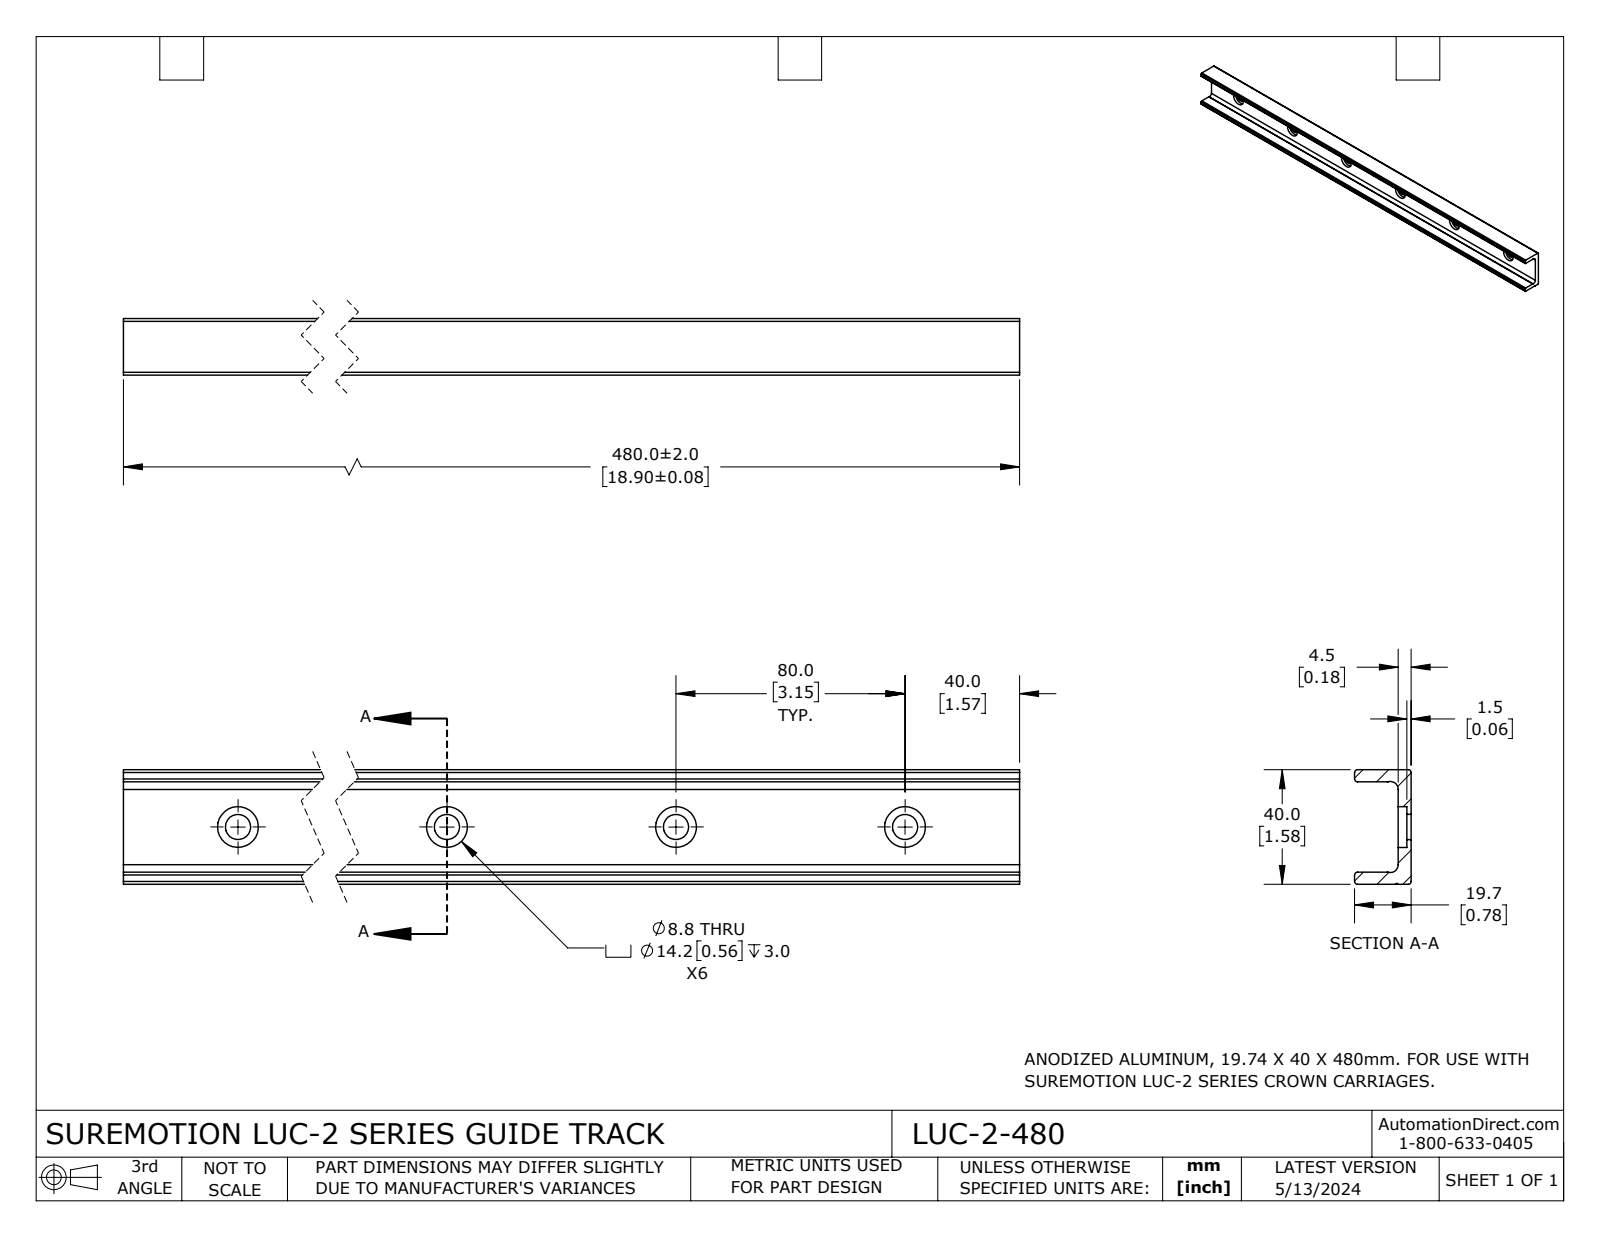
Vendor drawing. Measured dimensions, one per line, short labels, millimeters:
name: LUC-2-480
written by: SolidWorks 2023 (CONFIG_CONTROL_DESIGN)
unit: mm
bodies: 1 solid, 52 faces (17 planar, 35 cylindrical, 0 other)
size: 480 × 40.01 × 19.74
volume: 145 660 mm³; area: 70 907 mm²
holes: 6× ⌀8.81, 6× ⌀14.25
rounds: 8× R0.99, 2× R2.77, 1× R0.33
face distances: 4.5, 4.26, 35.76, 40.02, 31.5, 19.74, 15.24, 1.5, 3, 18.24
hole spacings: 80, 160, 240, 320, 400
